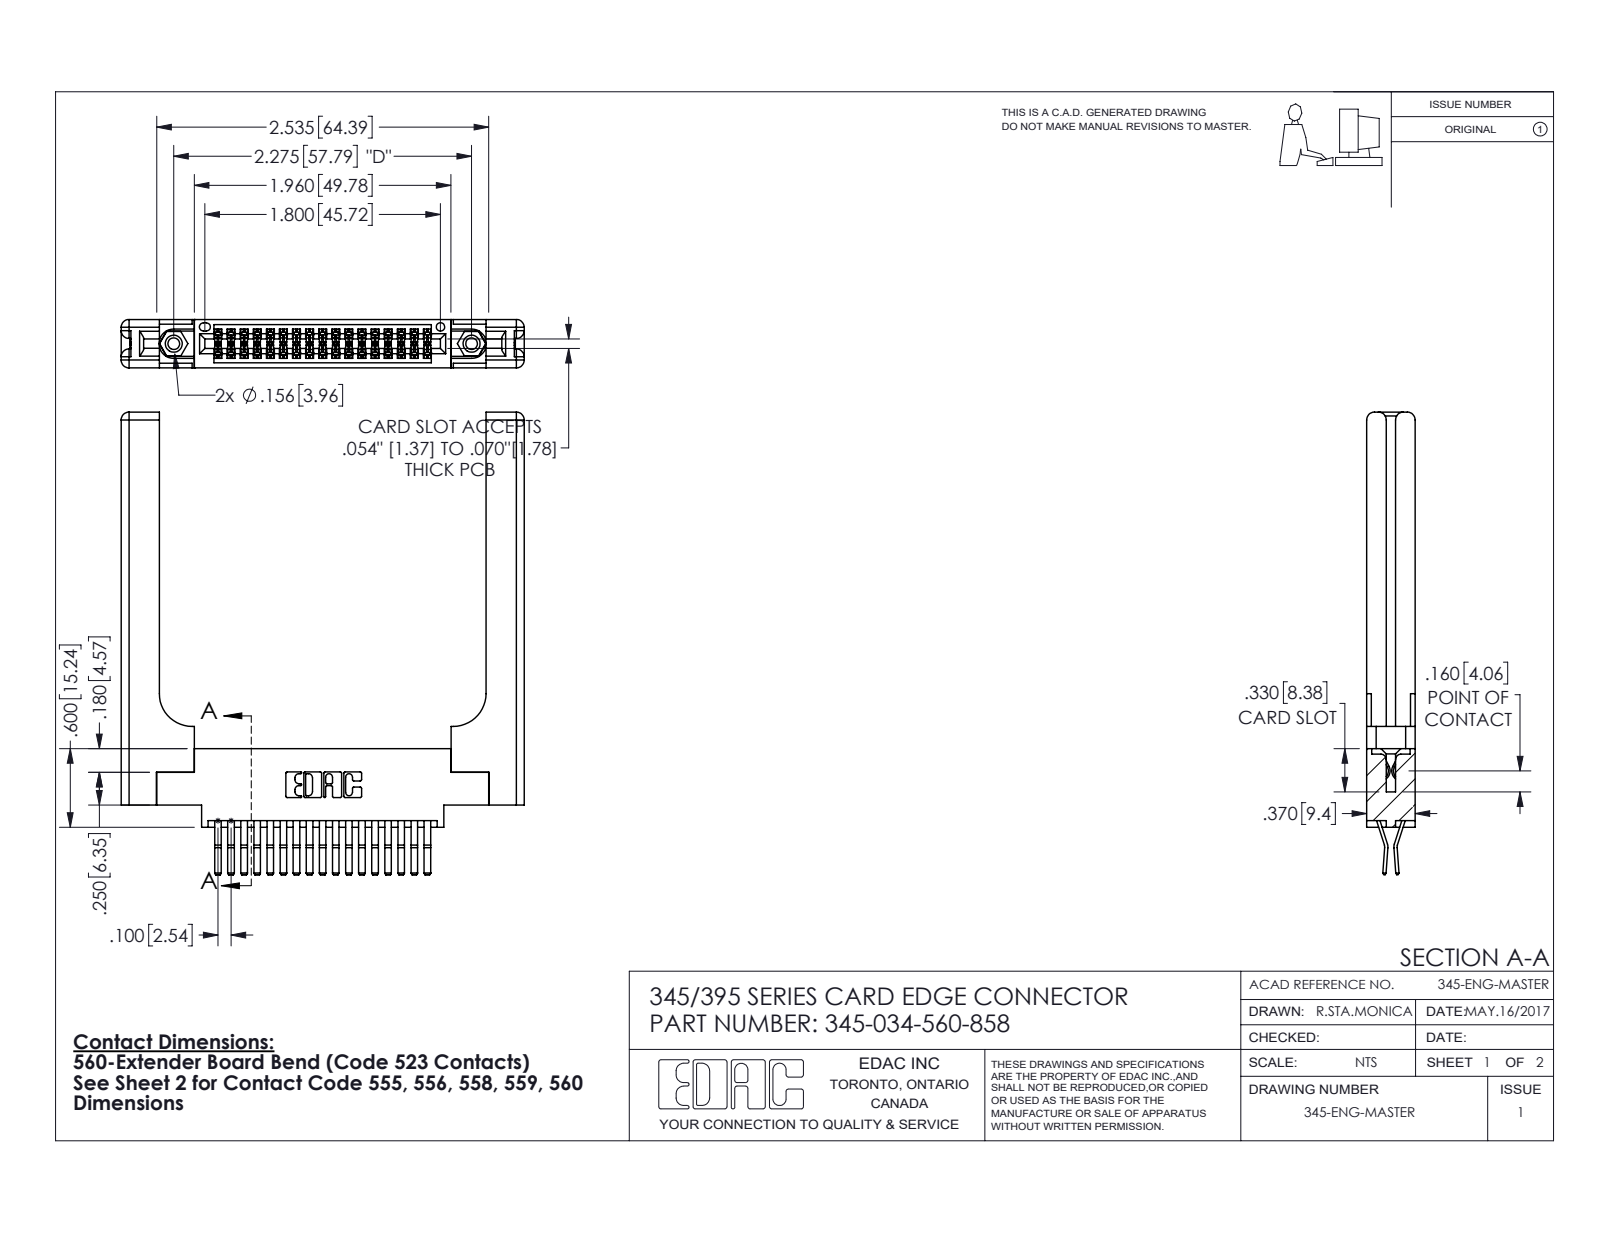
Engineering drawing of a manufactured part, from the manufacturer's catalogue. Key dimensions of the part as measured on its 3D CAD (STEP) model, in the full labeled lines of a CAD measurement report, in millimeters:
Part name (STEP PRODUCT): 345-292-001_560 Tail; 345 Part_0.170 Offset - 0.156 Dia-TH; 345-220-058_345-220-058; 345-034-560-858 (+1 more)
STEP written by: SolidWorks 2016 (CONFIG_CONTROL_DESIGN)
Units: millimetres
Bodies: 39 solids, 2154 faces (1354 planar, 740 cylindrical, 60 other)
Overall size (bounding box): 89.7 × 78.2 × 9.4
Volume: 15 900 mm³ · Surface area: 16 340 mm²
Round holes (diameter × count): ⌀2.3 ×2, ⌀3.2 ×2, ⌀4 ×2, ⌀1.6 ×1
Round bosses / shafts (diameter × count): ⌀3.9 ×2
Partial cylindrical surfaces — rounded edges, fillets, slot ends (radius × count): R0.2 ×51, R0.3 ×22, R1.5 ×16, R0.2 ×6, R0.8 ×6, R0.7 ×3, R0.3 ×2, R0.4 ×2
Main face-to-face distances: 9.4, 1.8, 7.6, 0.6, 3.8, 3.8, 2, 5.6, 5.7, 3.1
Hole centre spacings: 6.9, 51.8, 57.8
